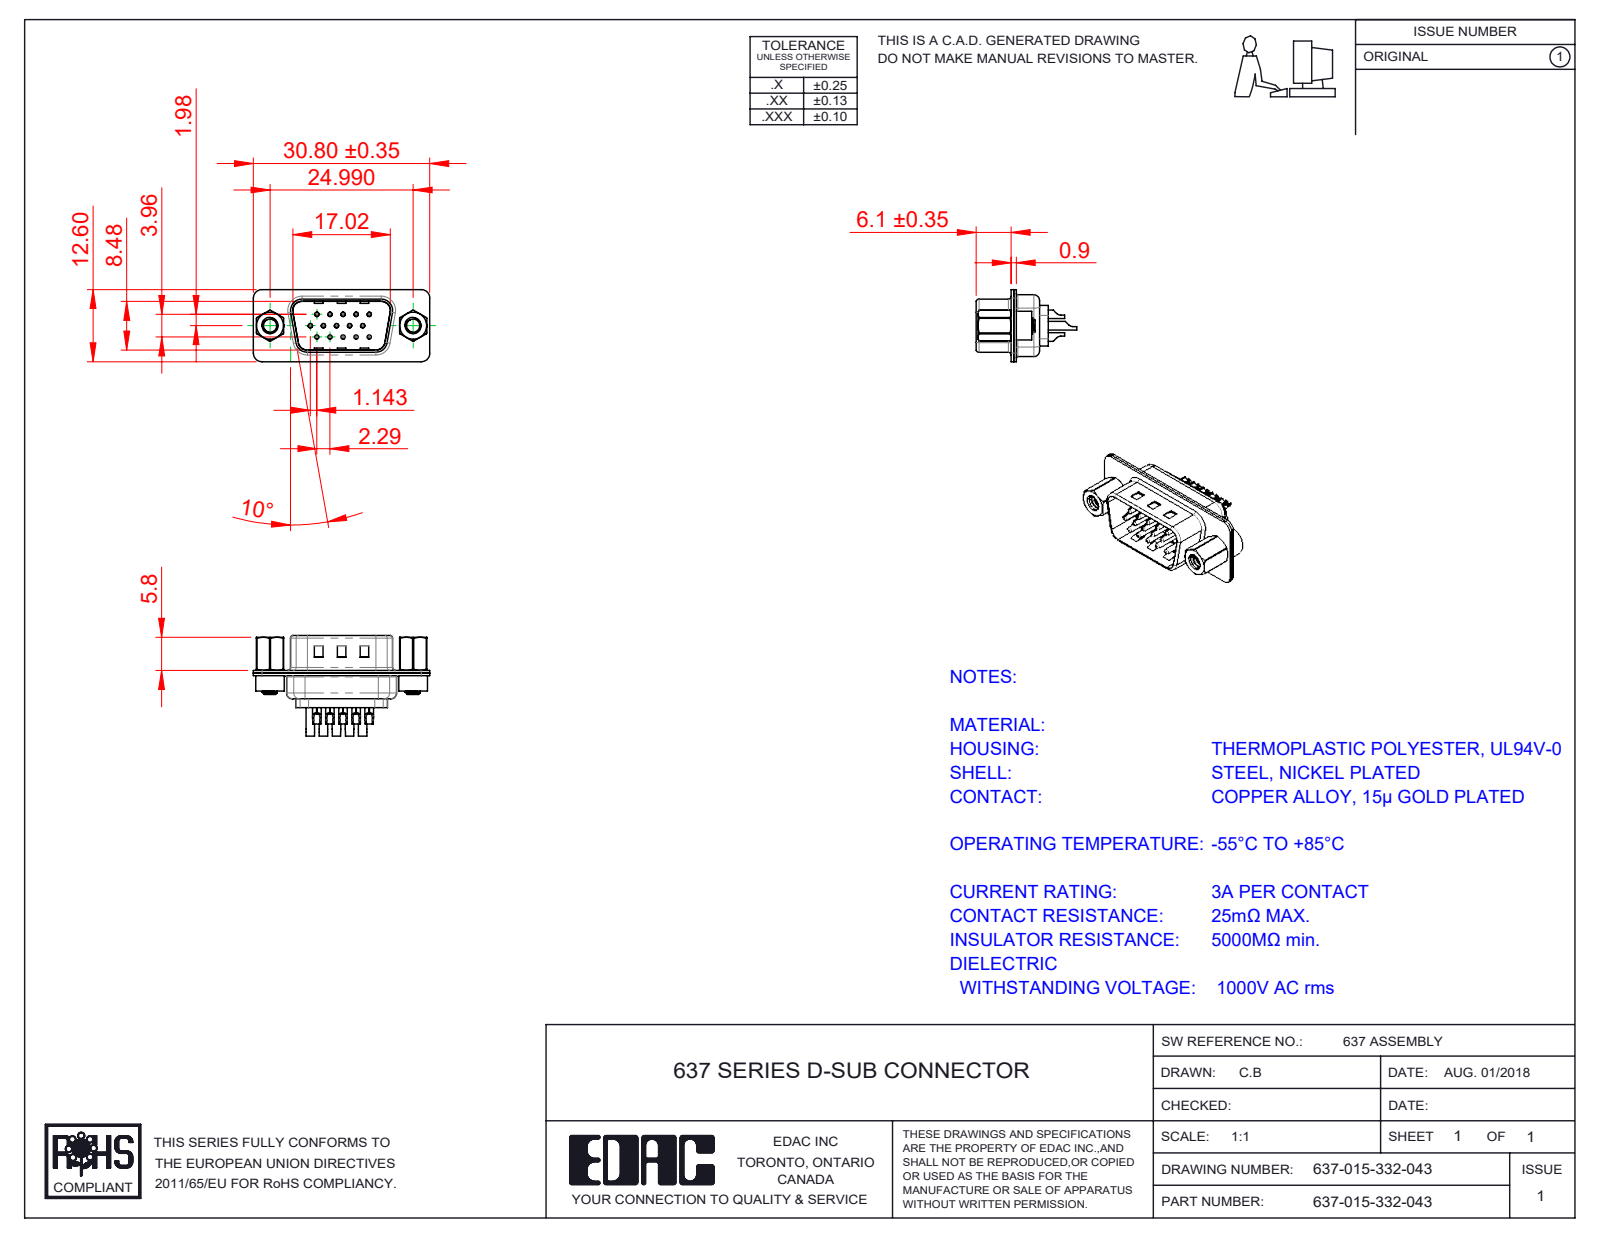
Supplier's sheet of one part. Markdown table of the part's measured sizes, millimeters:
| quantity | value |
| --- | --- |
| part name | 637 Contact Row 3_32; 637 Shell Rear_15 Contacts; 637 Housing_15 Contacts; 637 Contact Row 1_32 (+5 more) |
| STEP written by | SolidWorks 2020 (CONFIG_CONTROL_DESIGN) |
| units | millimeters |
| bodies | 22 solids, 1390 faces (339 planar, 636 cylindrical, 415 other) |
| overall size | 30.8 × 17.55 × 12.6 |
| volume | 1 544 mm³ |
| surface area | 5 262 mm² |
| round holes (diameter × count) | 0.35 × 15, 1.1 × 15, 1.6 × 15, 2.26 × 2, 2.29 × 2, 4 × 2, 4.8 × 2 |
| round bosses / shafts (diameter × count) | 2 × 15, 1.5 × 15, 0.75 × 15, 5 × 2, 4.9 × 2, 2.79 × 2 |
| partial cylindrical surfaces (radius × count) | 1.5 × 16, 2 × 12, 0.5 × 8, 1 × 7, 0.25 × 4, 0.55 × 4, 0.7 × 4, 0.95 × 4 |
| main face-to-face distances | 0.45, 0.9, 0.4, 0.7, 8.88, 8.48, 1.05, 0.31, 4.55, 6.5 |
| hole center spacings | 3.96, 2.28, 4.57, 2.29, 6.05, 6.86, 7.92, 6.04 |
